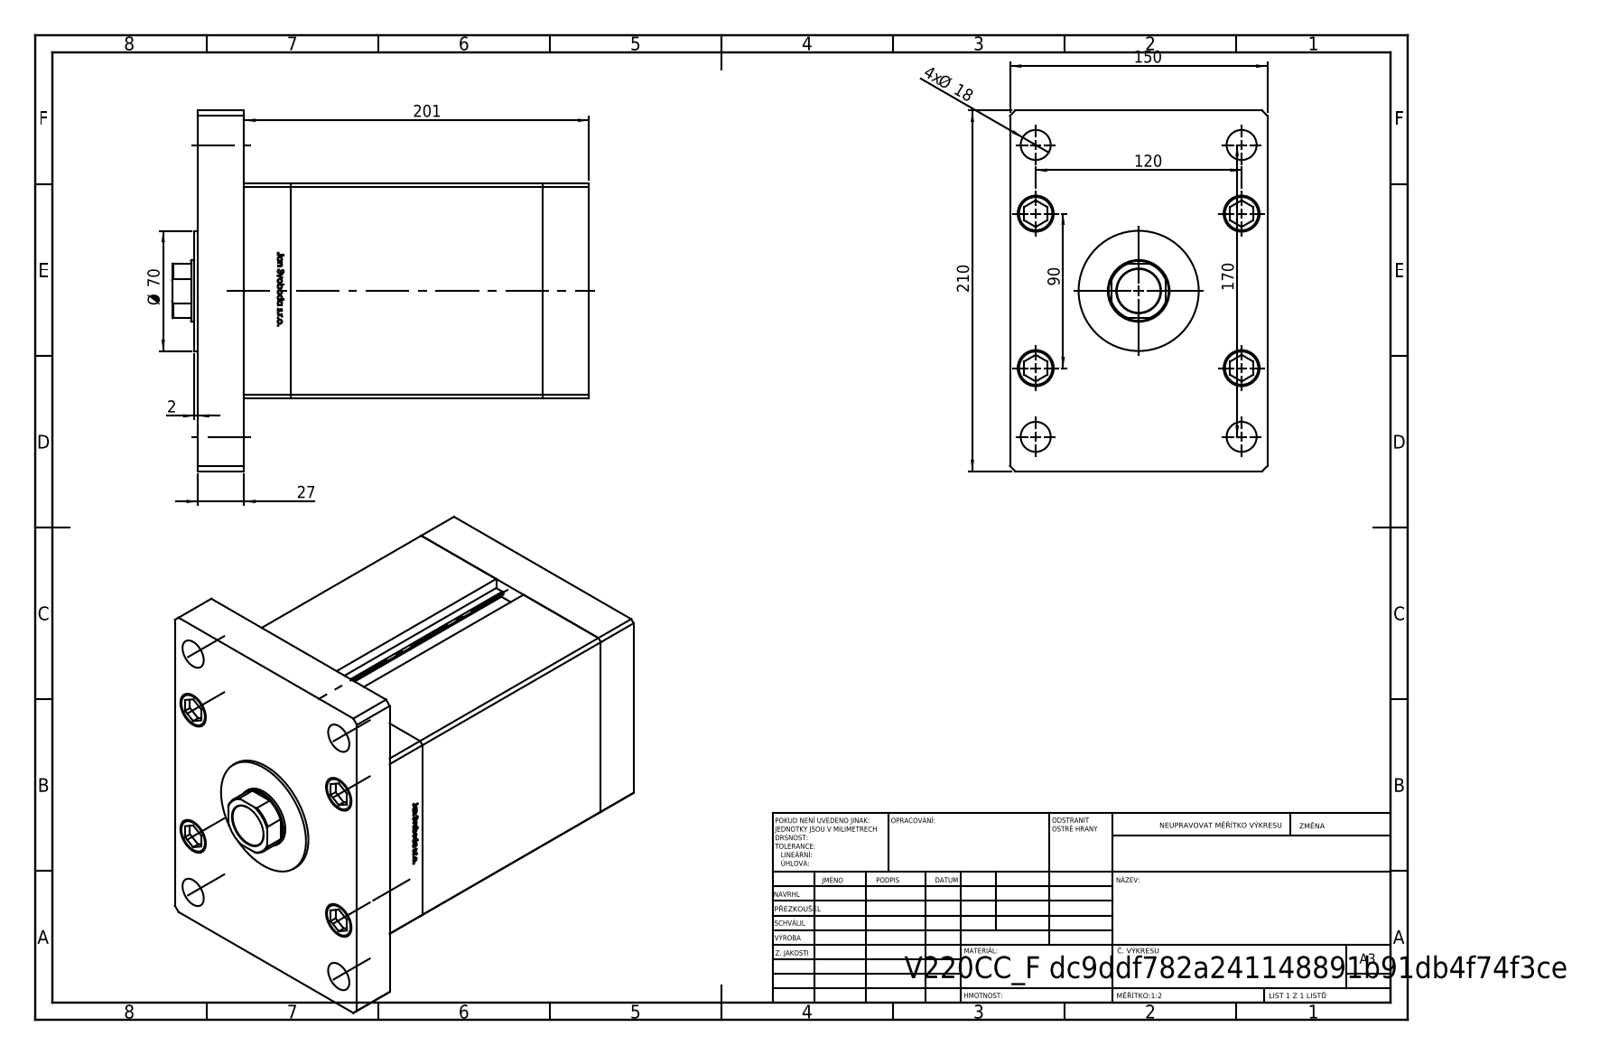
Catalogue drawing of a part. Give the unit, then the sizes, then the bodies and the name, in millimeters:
Units: millimetres
Overall size (bounding box): 243 × 210 × 150
Round holes (diameter × count): ⌀17.5 ×9, ⌀22 ×5, ⌀16 ×4, ⌀21 ×4, ⌀2 ×2, ⌀13.16 ×2, ⌀25.5 ×1, ⌀36 ×1, ⌀37.5 ×1
Round bosses / shafts (diameter × count): ⌀8 ×9, ⌀21 ×5, ⌀80 ×1, ⌀70 ×1
Partial cylindrical surfaces — rounded edges, fillets, slot ends (radius × count): R0.93 ×2, R17.5 ×1
Main face-to-face distances: 27, 174, 201, 150, 147, 54, 125, 167.5, 228, 33.5
Hole centre spacings: 51, 40, 75, 104.04, 120, 126.49, 130, 176.92
Volume: 4 072 000 mm³ · Surface area: 453 403 mm²
Bodies: 19 solids, 1310 faces (517 planar, 187 cylindrical, 606 other)
Part name (STEP PRODUCT): ALLEN BOLT; V220C_FRONT_F; V220C_F; V220C_VC_F (+2 more)
STEP written by: SolidWorks 2019 (CONFIG_CONTROL_DESIGN)
